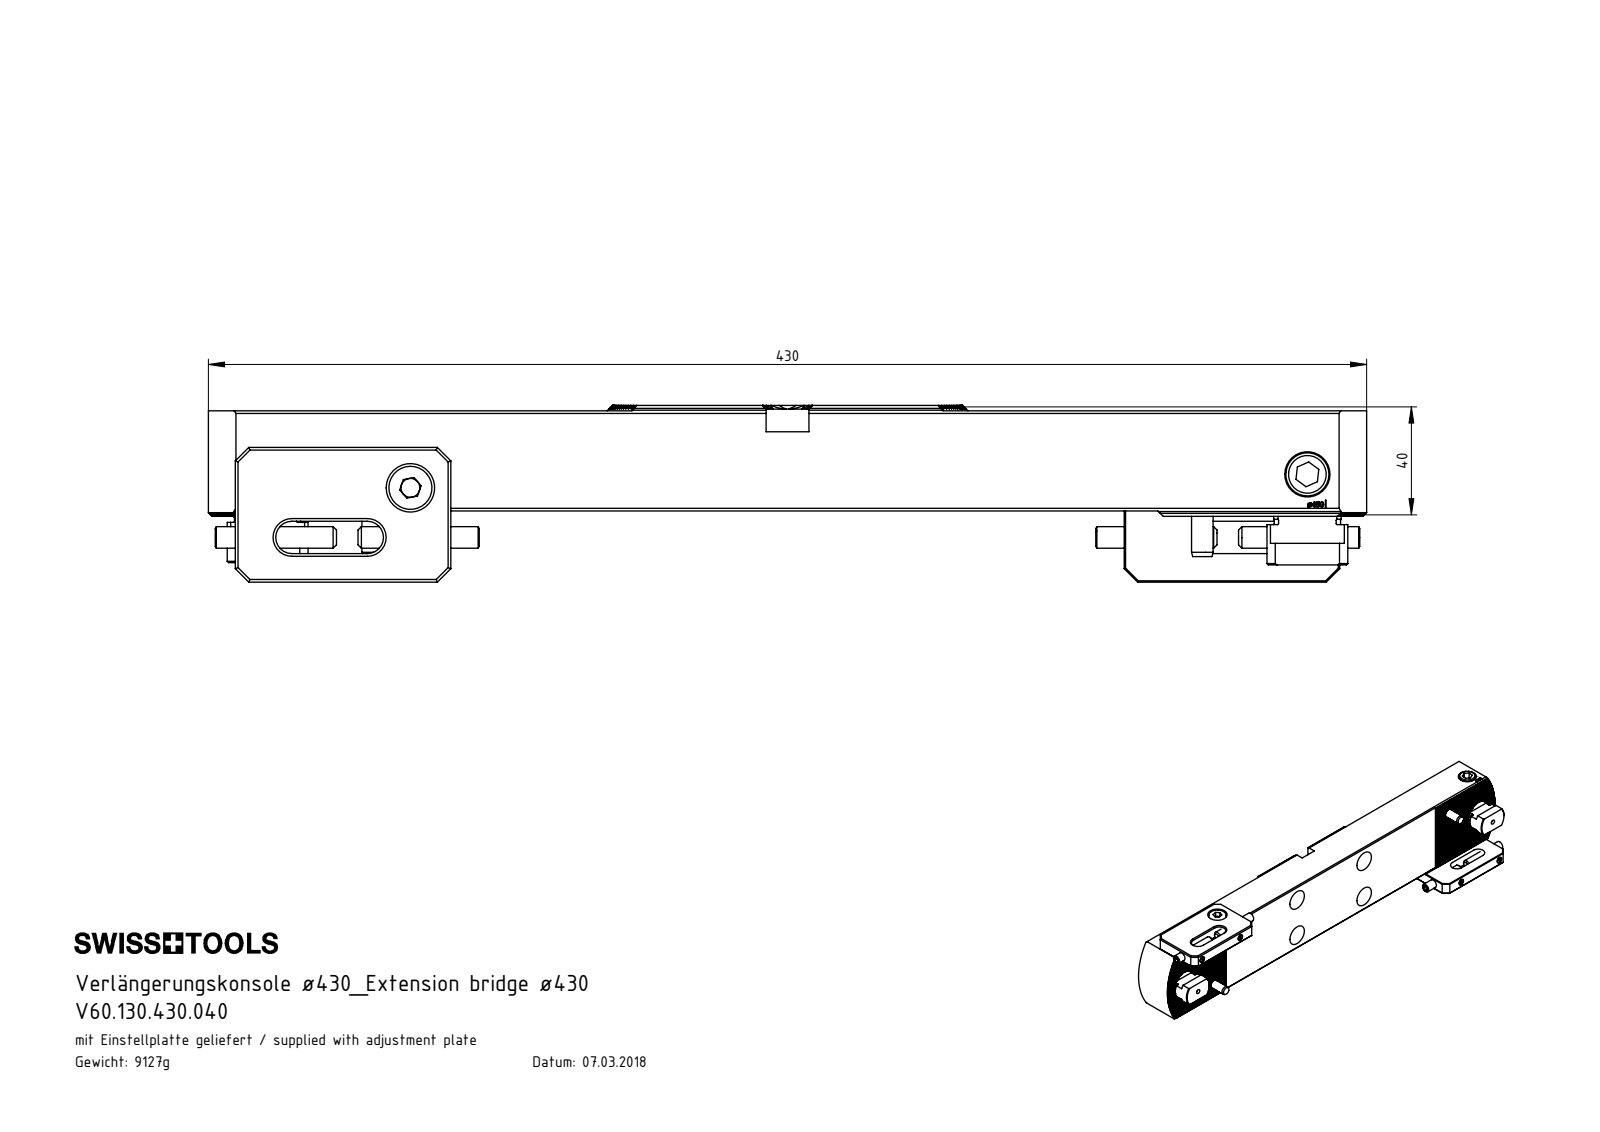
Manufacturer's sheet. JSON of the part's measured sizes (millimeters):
{"part_name": "DIN 7984 - M10 x 16; VK1-ER2.101.010_A; VK1-ER7.001.012_B; Ko1.VK1.430.040 (+8 more)", "step_written_by": "SolidWorks 2017 (AUTOMOTIVE_DESIGN)", "units": "millimeters", "bodies": {"solids": 27, "faces": 1331, "planar": 890, "cylindrical": 260, "other": 181}, "overall_size": [430, 94, 65.58], "volume_mm3": 1169000, "surface_area_mm2": 176819, "round_holes": [[5, 4], [6, 4], [6.8, 4], [13, 4], [19, 4], [2, 2], [8, 2], [8.5, 2], [10.5, 2], [11, 2], [14, 2], [18, 2]], "round_bosses_or_shafts": [[16, 4], [6, 4], [10, 2], [8, 2]], "partial_cylinders_radius": [[0.14, 66], [2, 8], [6, 4], [12.3, 2], [15, 2], [65, 2], [7.95, 1]], "face_to_face_distances": [37.16, 70, 12, 82, 1.73, 8.66, 3.46, 6.93, 0.5, 41.57], "hole_center_spacings": [150.34, 237.84, 386, 7.9, 18.55, 19.61, 34.53, 35.09]}
